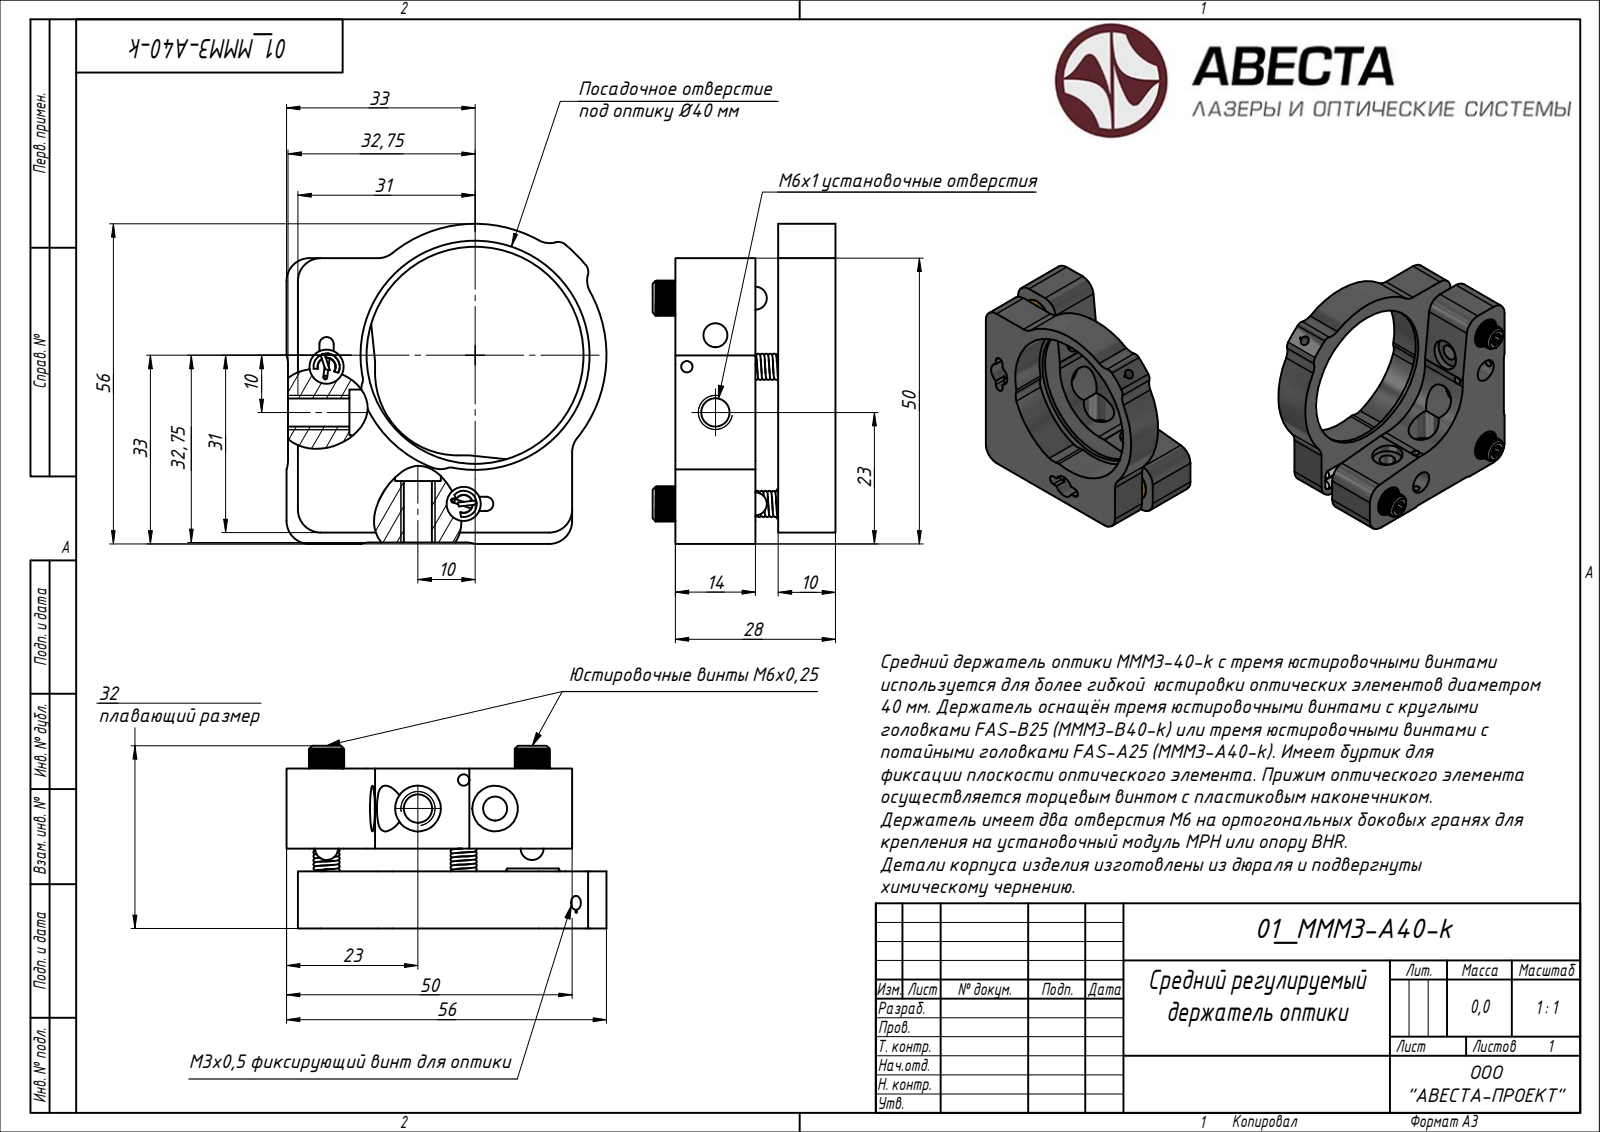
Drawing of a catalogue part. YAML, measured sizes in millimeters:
step_written_by: "ST-DEVELOPER v15 (AUTOMOTIVE_DESIGN)"
units: millimeters
bodies: {solids: 11, faces: 293, planar: 112, cylindrical: 0, other: 181}
overall_size: [56, 56, 31]
volume: 28367
surface_area: 17501
face_to_face_distances: [14, 10, 4, 18, 28, 2, 1.75, 48, 49.75, 50]
